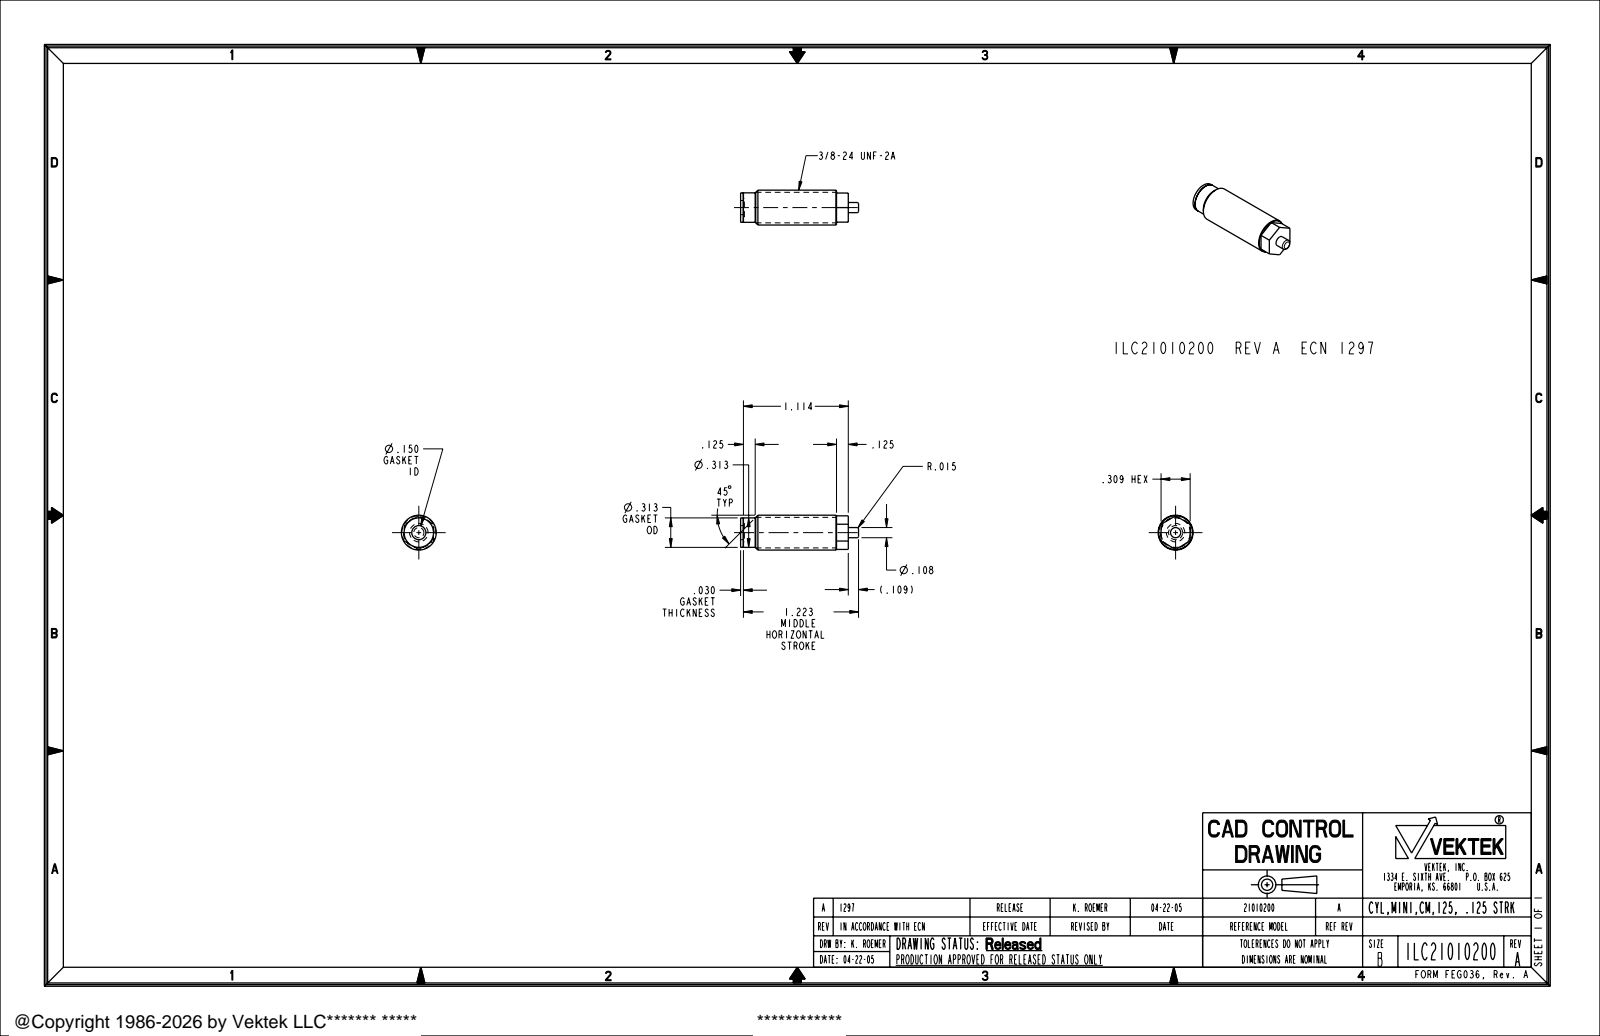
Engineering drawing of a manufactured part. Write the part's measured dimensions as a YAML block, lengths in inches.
part_name: "ILC21010200"
step_written_by: "PRO/ENGINEER BY PARAMETRIC TECHNOLOGY CORPORATION, 2004290 (AUTOMOTIVE_DESIGN_CC2)"
units: inches
bodies: {solids: 2, faces: 34, planar: 14, cylindrical: 14, other: 6}
overall_size: [1.253, 0.37, 0.37]
volume: 0.115
surface_area: 2.612
round_holes:
  - {diameter: 0.15, count: 1}
  - {diameter: 0.196, count: 1}
round_bosses_or_shafts:
  - {diameter: 0.37, count: 1}
  - {diameter: 0.324, count: 1}
  - {diameter: 0.313, count: 1}
  - {diameter: 0.108, count: 1}
face_to_face_distances: [0.125, 0.309, 0.029, 1.019, 1.144, 0.99, 1.115, 0.03, 0.989, 1.114]
